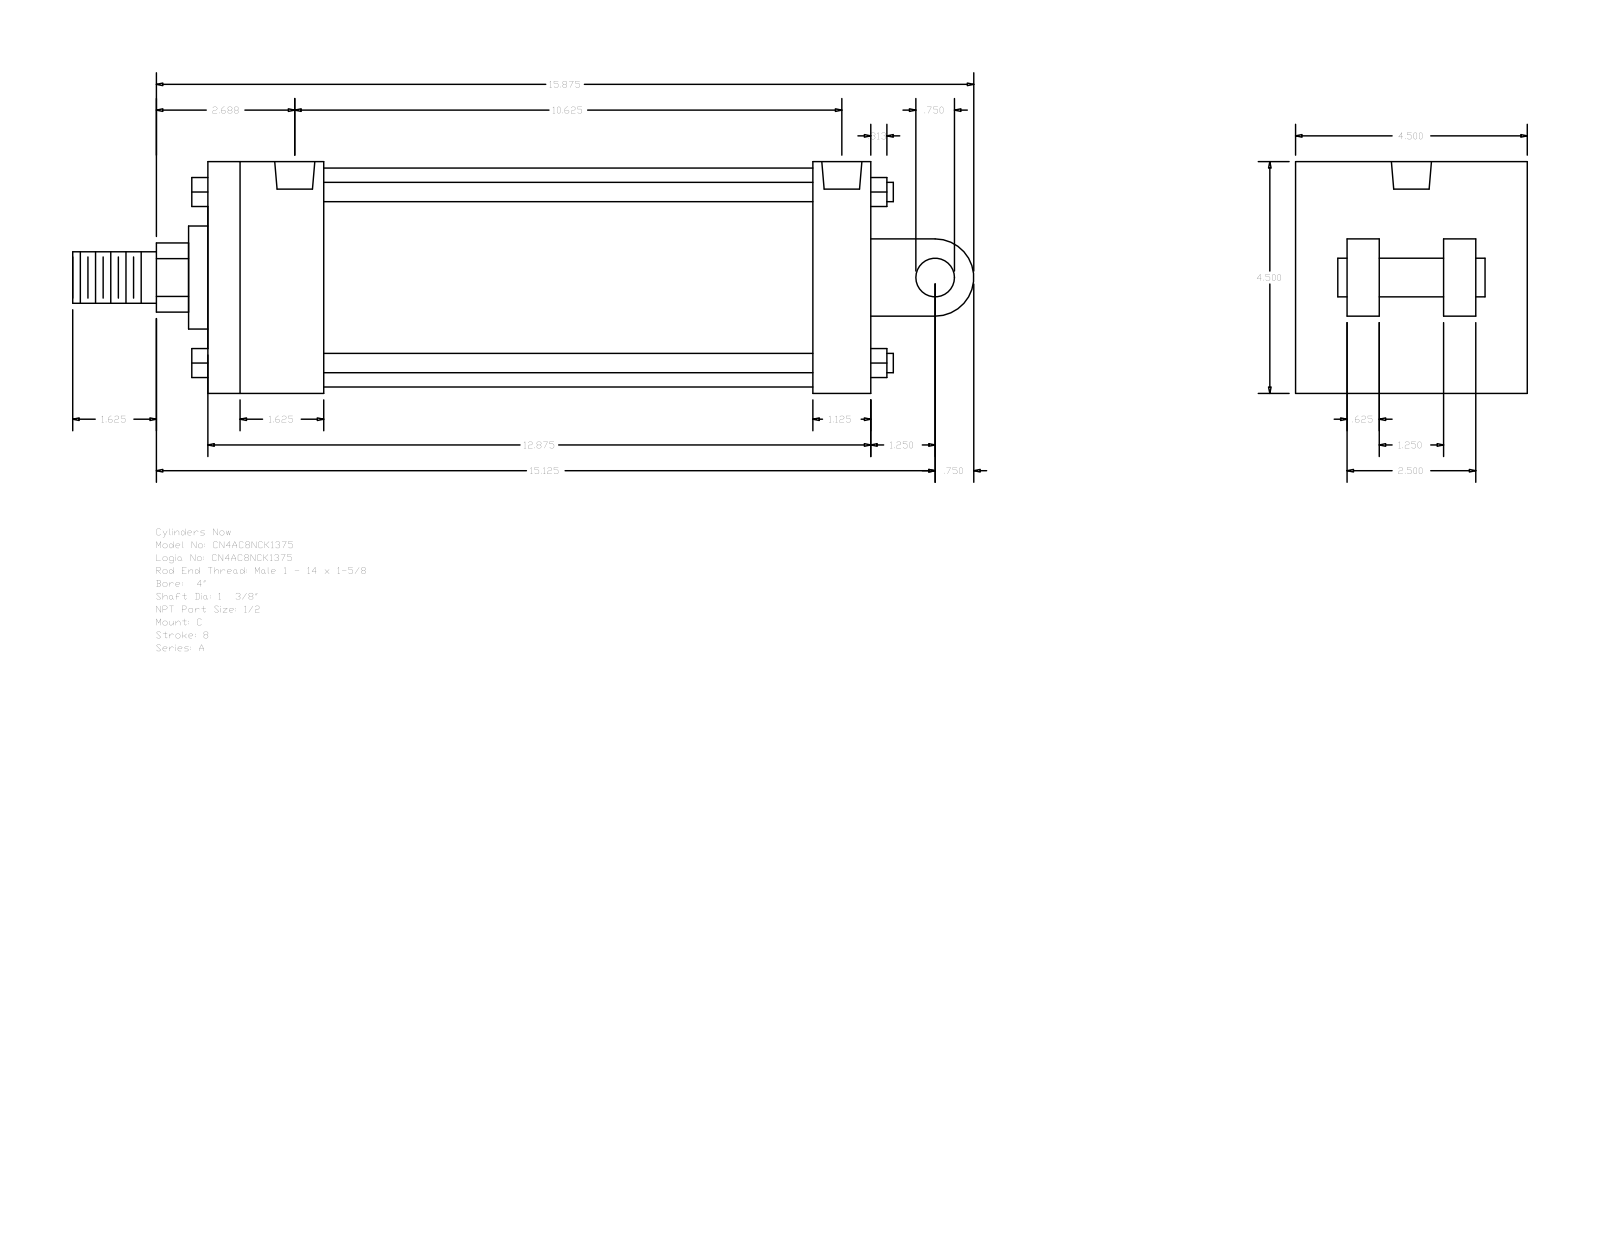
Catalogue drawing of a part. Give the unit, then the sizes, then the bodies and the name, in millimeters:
Units: millimetres
Overall size (bounding box): 444.5 × 114.3 × 114.3
Round holes (diameter × count): ⌀8.73 ×4, ⌀19.77 ×2
Round bosses / shafts (diameter × count): ⌀9.53 ×4, ⌀107.95 ×1, ⌀50.8 ×1, ⌀34.92 ×1, ⌀25.4 ×1, ⌀19.05 ×1
Partial cylindrical surfaces — rounded edges, fillets, slot ends (radius × count): R17.06 ×1, R19.05 ×1
Main face-to-face distances: 114.3, 327.03, 57.15, 28.58, 73.03, 298.45, 241.3, 269.88, 41.27, 25.4
Hole centre spacings: 3.18, 263.52, 266.7, 269.88
Bodies: 0 solids, 135 faces (102 planar, 33 cylindrical, 0 other)
Part name (STEP PRODUCT): A_C__0400_1.375
STEP written by: GSSL Pune (CONFIG_CONTROL_DESIGN)
